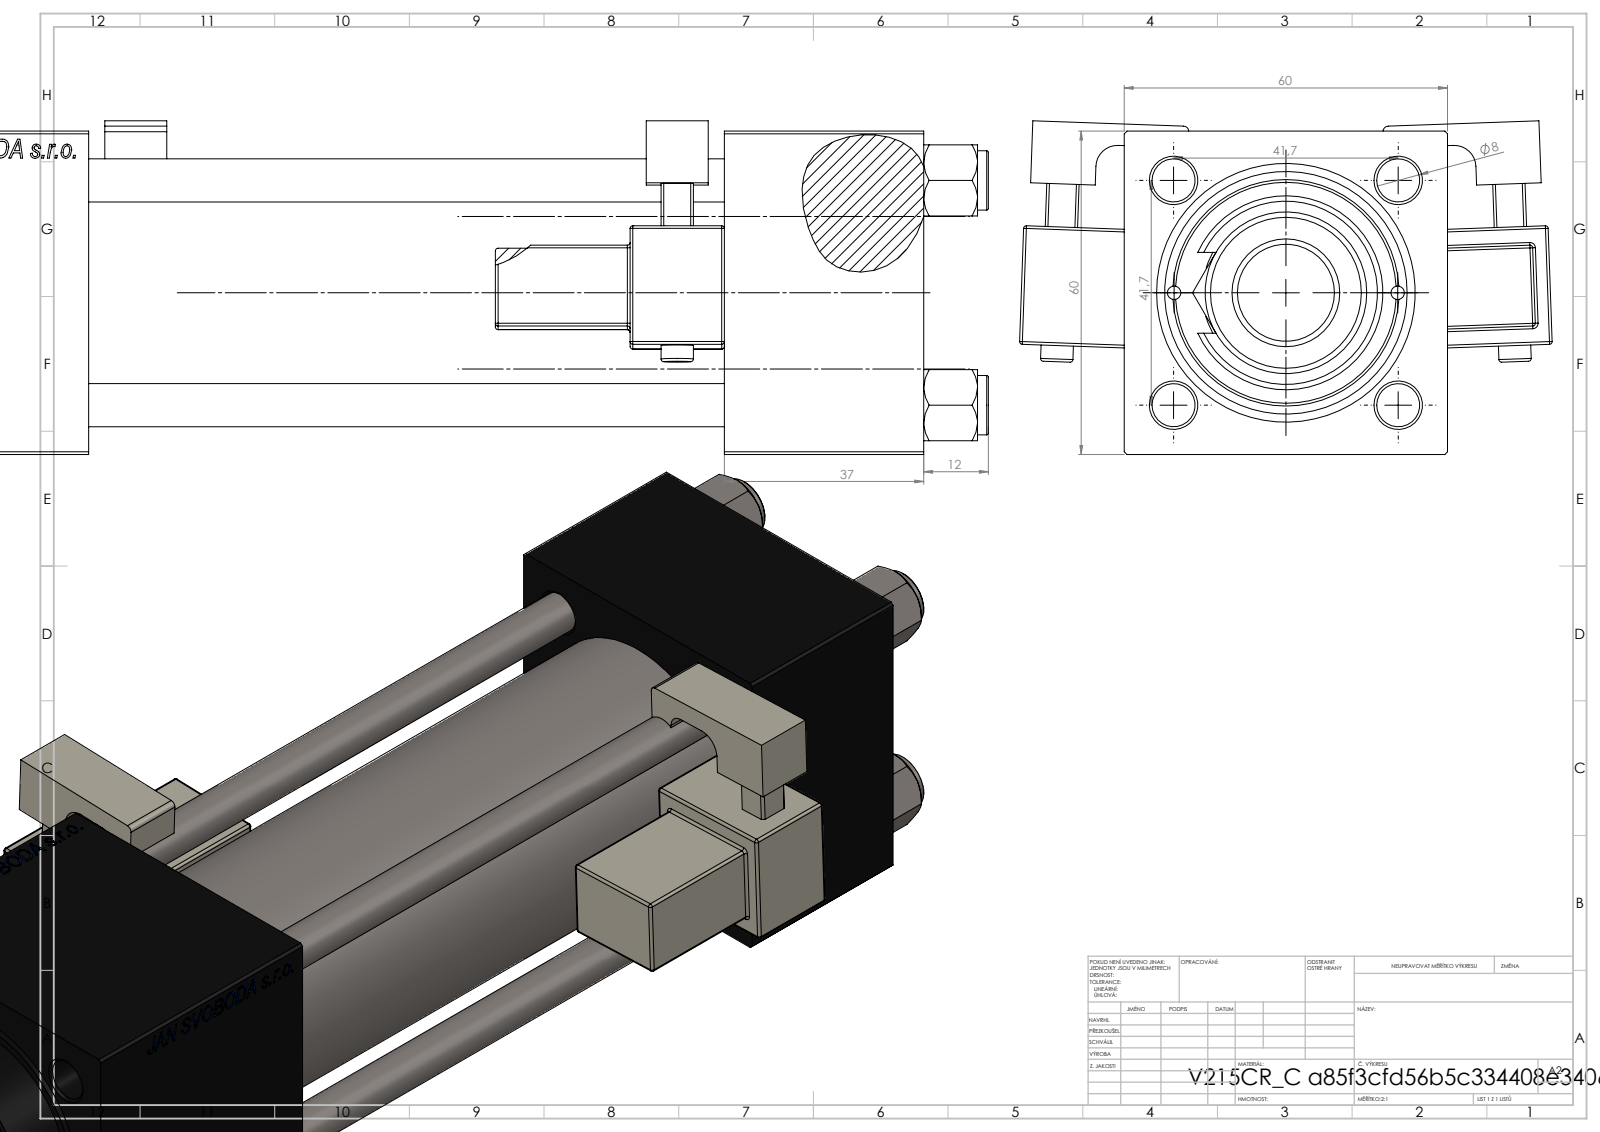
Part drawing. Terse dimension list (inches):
name: V215CR_VCP_C; V215CR_C_TYCINKA; NUT_M5_C; V215_VC_A (+4 more)
written by: SolidWorks 2019 (CONFIG_CONTROL_DESIGN)
unit: in
bodies: 15 solids, 1393 faces (614 planar, 163 cylindrical, 616 other)
size: 12.953 × 3.892 × 2.437
volume: 35.83 in³; area: 254.8 in²
holes: 4× ⌀0.315, 2× ⌀0.098, 2× ⌀0.276, 2× ⌀0.656, 2× ⌀0.945, 1× ⌀0.728, 1× ⌀1.102, 1× ⌀1.22, 1× ⌀1.575, 1× ⌀1.772
bosses: 4× ⌀0.433, 2× ⌀0.236, 1× ⌀1.811, 1× ⌀1.654, 1× ⌀1.417, 1× ⌀1.181, 1× ⌀0.866, 1× ⌀0.787
rounds: 48× R0.02, 2× R0.039, 2× R0.098, 2× R0.157, 1× R0.295, 1× R0.472, 1× R0.531
face distances: 2.362, 1.457, 6.102, 4.646, 2.087, 0.591, 7.059, 5.602, 0.957, 8.189
hole spacings: 0.821, 1.161, 1.642, 1.832, 0.817, 2.322, 1.634, 6.004
